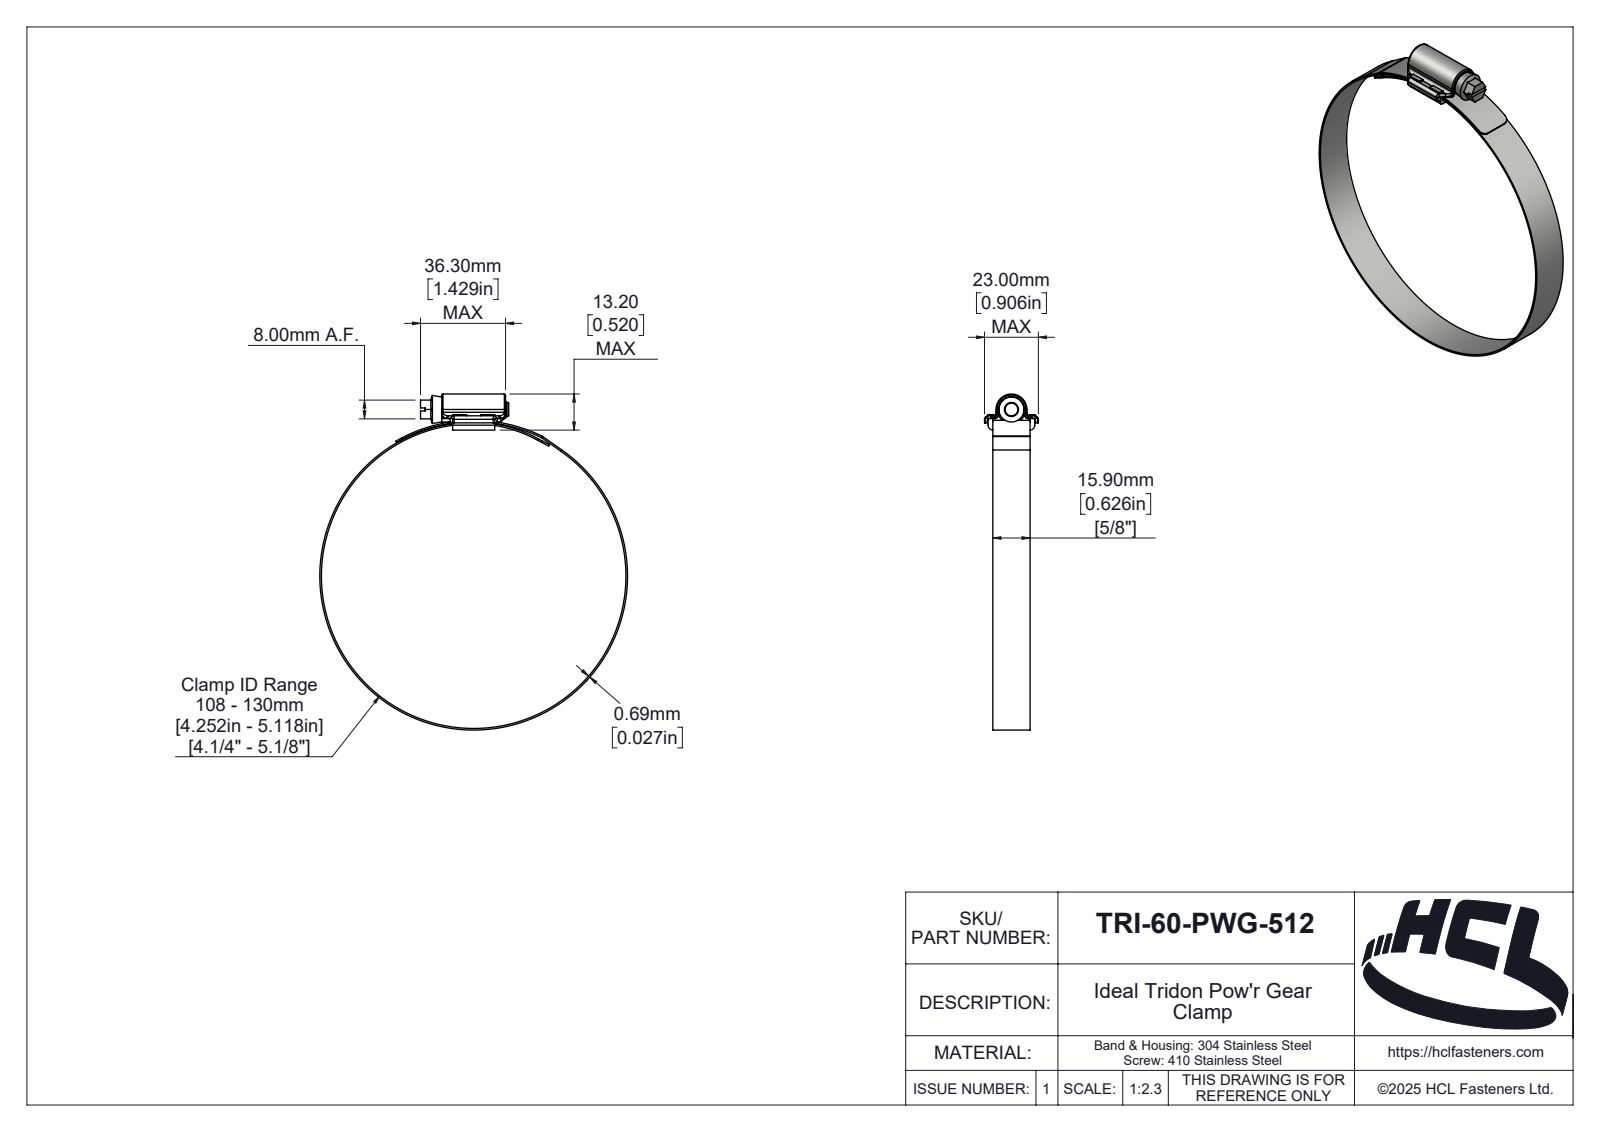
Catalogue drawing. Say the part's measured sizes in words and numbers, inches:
The part is named "TRI-60-PWG-512". Its 3-D file was written by "SolidWorks 2025 (AUTOMOTIVE_DESIGN)". It is 4 solids with 268 faces: 87 planar, 102 cylindrical and 79 other. Overall it measures 5.645 by 5.172 by 0.906 inches. Its volume is 0.638 cubic inches and its surface area 31.8 square inches. Round holes: 1 of diameter 5.118. Round bosses or shafts: 1 of diameter 5.172, 1 of diameter 0.421, 1 of diameter 0.236. Partial cylindrical surfaces (rounded edges, fillets, slot ends): 14 of radius 0.039, 4 of radius 0.02, 4 of radius 0.059, 3 of radius 0.079, 2 of radius 0.004, 2 of radius 0.083, 2 of radius 0.118, 1 of radius 0.018. The main face-to-face distances are 0.079, 0.626, 0.705, 0.193, 0.027, 0.047, 0.179, 0.132, 0.604, 0.1.
